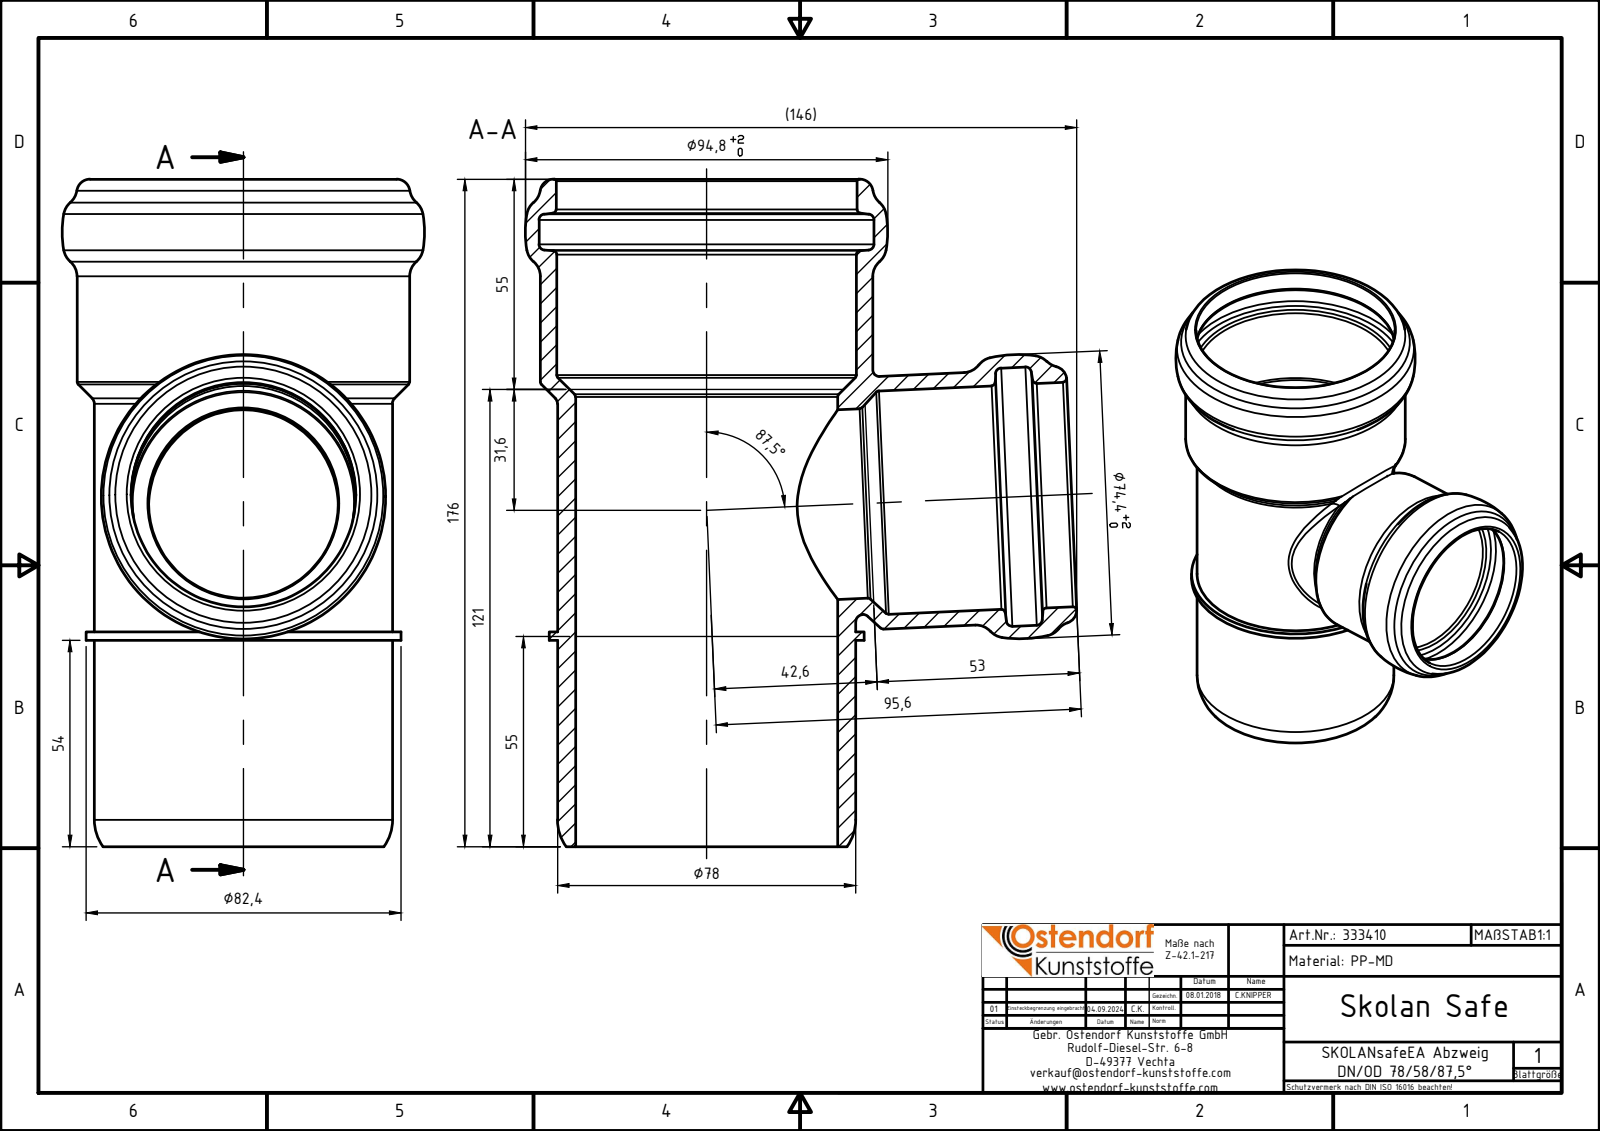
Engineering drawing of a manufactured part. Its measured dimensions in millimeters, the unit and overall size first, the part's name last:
Units: millimetres
Overall size (bounding box): 174.61 × 144.24 × 94.8
Round holes (diameter × count): ⌀49.6 ×1, ⌀58.5 ×1, ⌀58.8 ×1, ⌀67.6 ×1, ⌀68.6 ×1, ⌀78.4 ×1, ⌀78.7 ×1, ⌀87.6 ×1
Round bosses / shafts (diameter × count): ⌀87 ×1, ⌀82.4 ×1, ⌀78 ×1, ⌀66.1 ×1, ⌀58 ×1
Main face-to-face distances: 2.2, 54, 56.2
Volume: 239 817 mm³ · Surface area: 112 628 mm²
Bodies: 1 solid, 59 faces (3 planar, 15 cylindrical, 41 other)
Part name (STEP PRODUCT): 333410z
STEP written by: Autodesk Inventor 2024 (AUTOMOTIVE_DESIGN)
